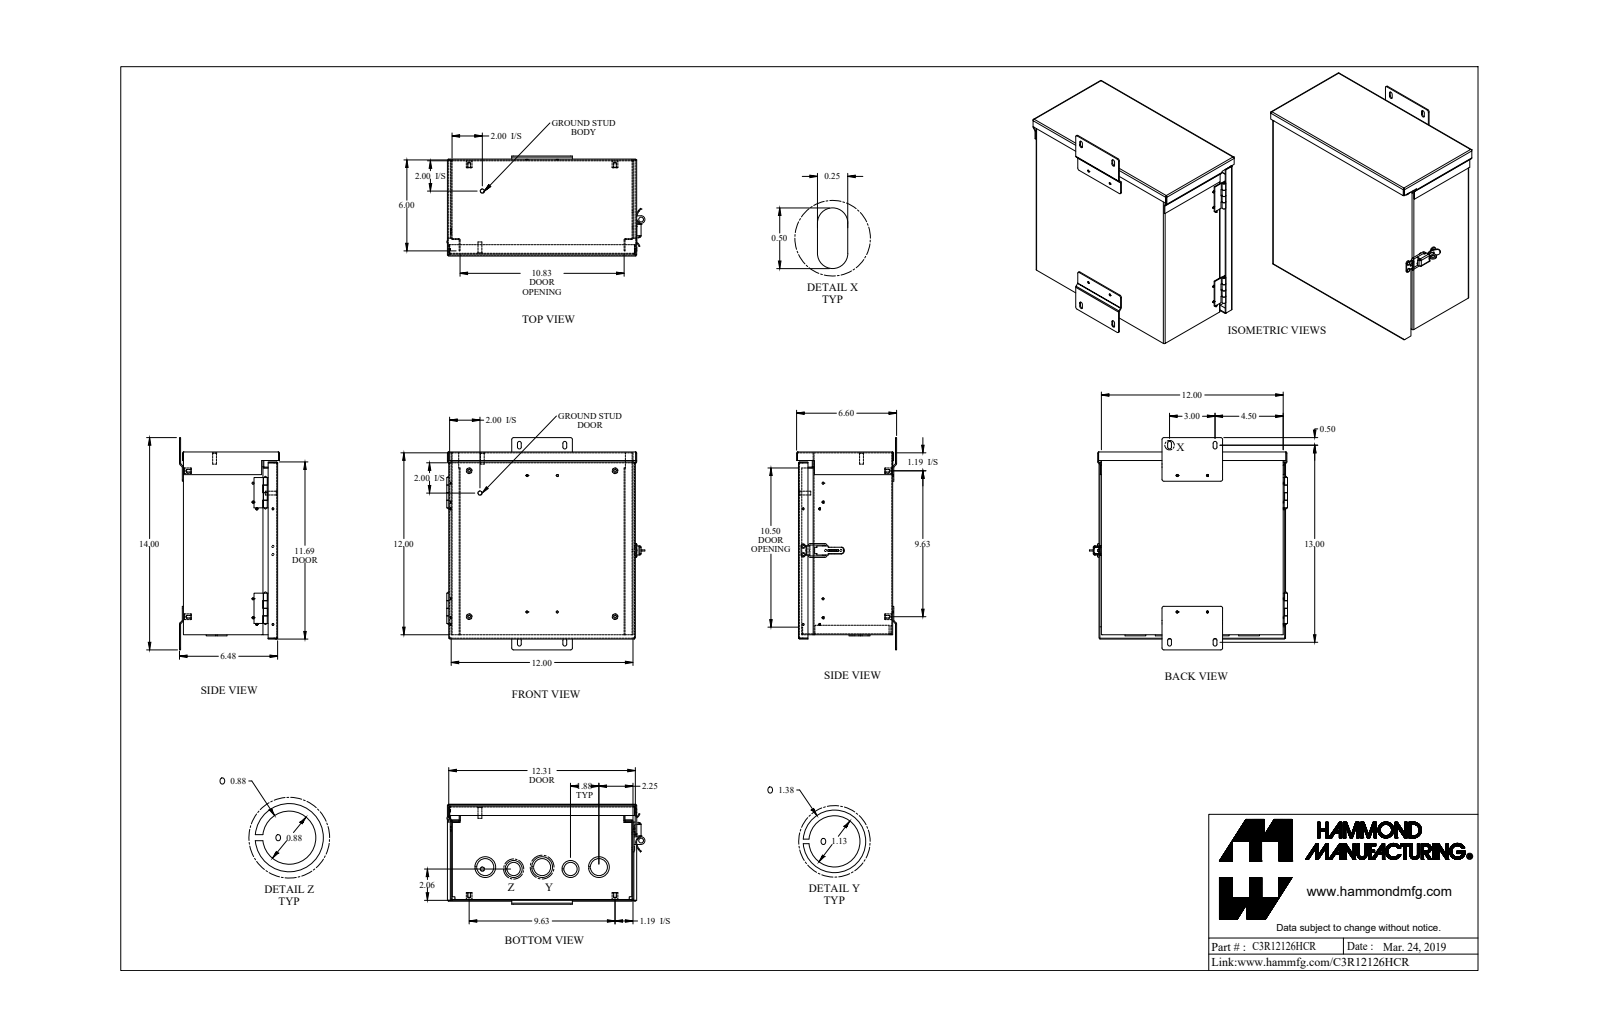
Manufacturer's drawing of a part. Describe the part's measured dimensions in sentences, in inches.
The part is named "C3R12126HCR_Default". Its 3-D file was written by "SolidWorks 2019 (CONFIG_CONTROL_DESIGN)". It is 31 solids with 851 faces: 499 planar, 297 cylindrical and 55 other. Overall it measures 14 by 13.07 by 6.599 inches. Its volume is 48.36 cubic inches and its surface area 1 561 square inches. Round holes: 4 of diameter 0.137, 4 of diameter 0.14, 4 of diameter 0.156, 3 of diameter 1.125, 2 of diameter 0.133, 2 of diameter 0.145, 2 of diameter 0.875, 1 of diameter 0.125, 1 of diameter 0.13, 1 of diameter 0.313. Round bosses or shafts: 12 of diameter 0.131, 4 of diameter 0.1, 3 of diameter 0.125, 2 of diameter 1.375, 2 of diameter 1.125, 2 of diameter 0.375, 2 of diameter 0.375, 2 of diameter 0.281. Partial cylindrical surfaces (rounded edges, fillets, slot ends): 28 of radius 0.029, 28 of radius 0.086, 21 of radius 0.125, 6 of radius 0.036, 6 of radius 0.108, 2 of radius 0.135, 1 of radius 0.04, 1 of radius 0.068. The main face-to-face distances are 0.057, 6.16, 12, 11.943, 6.103, 6.217, 12.057, 11.886, 0.187, 0.244. The hole center spacings are 9.625, 1.498, 3.75, 1.01, 1.01, 1.879, 1.88, 2.
